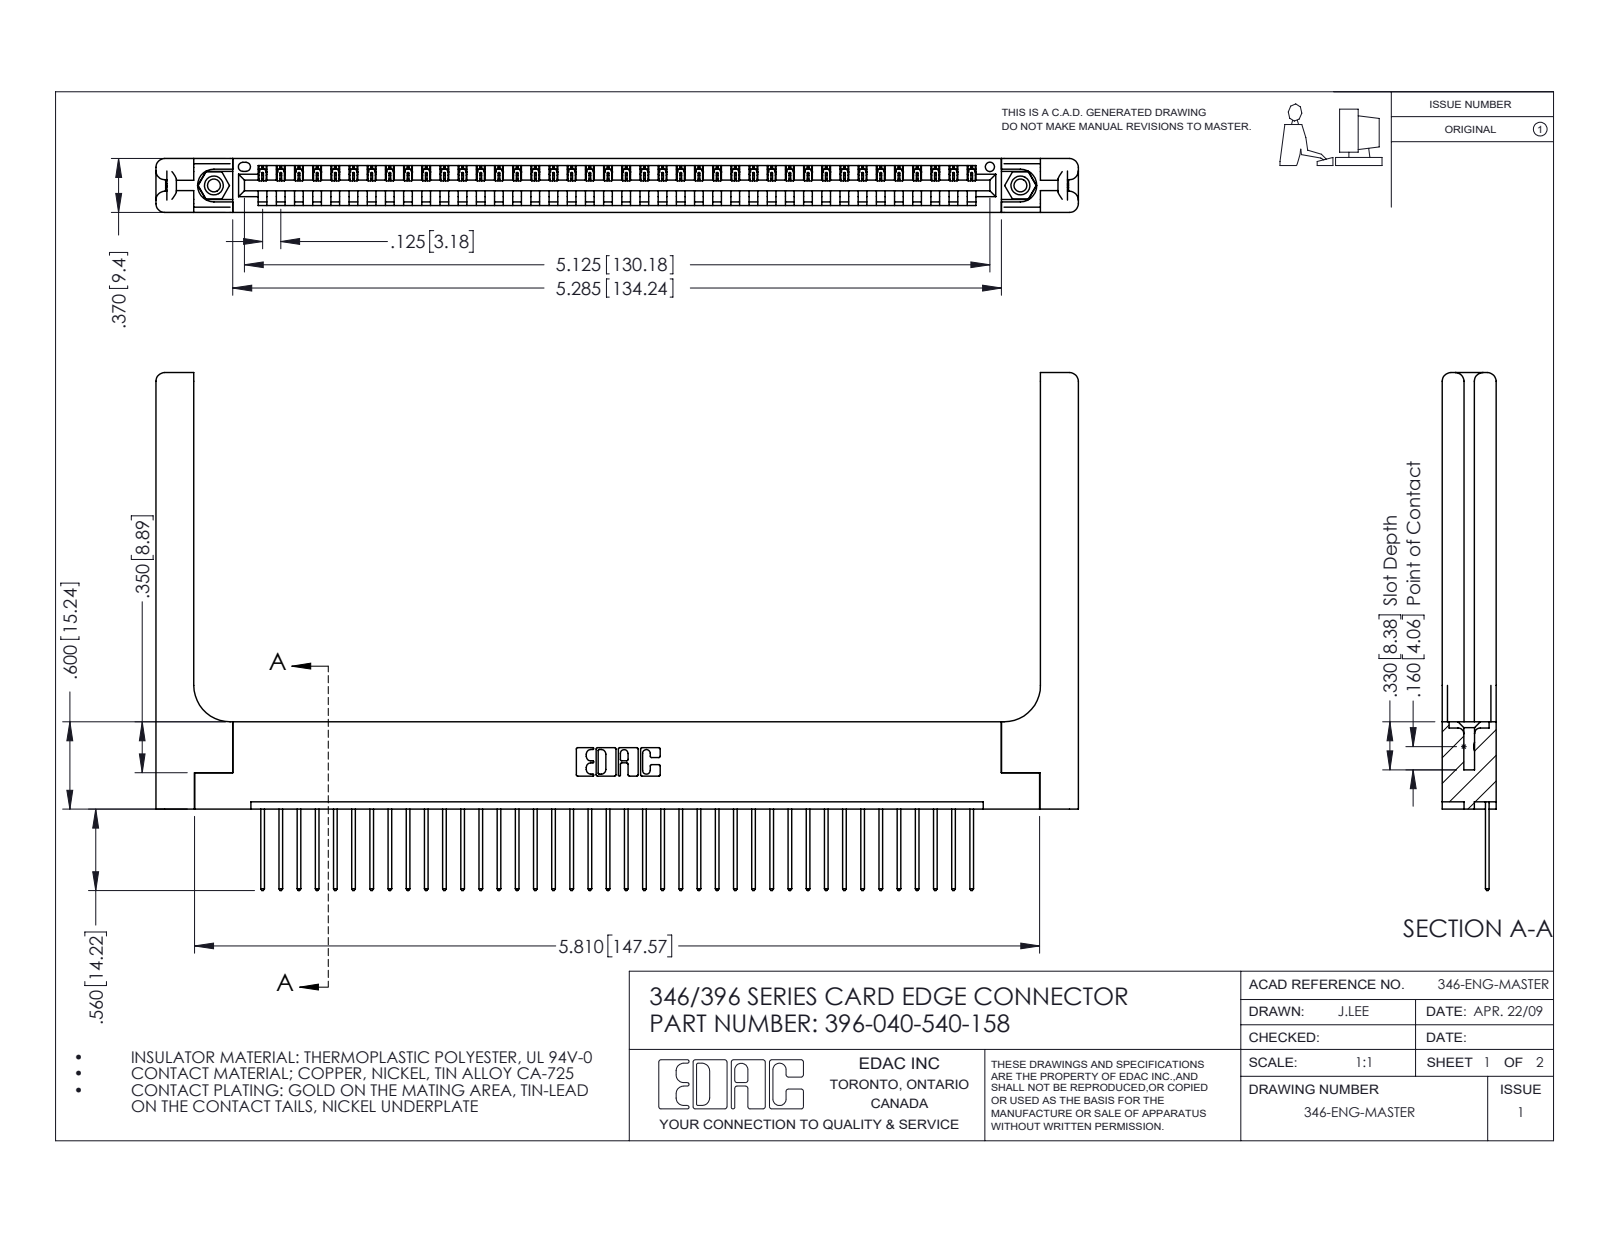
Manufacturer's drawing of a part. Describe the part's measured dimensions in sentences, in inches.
The part is named "345-292-001_345-293-140; 346 Part_Flush Mounting Lugs - 0.156 Dia-TH; 396-040-540-158; 345-250-001_345-250-001-102 (+1 more)". Its 3-D file was written by "SolidWorks 2016 (CONFIG_CONTROL_DESIGN)". It is 45 solids with 2698 faces: 1824 planar, 814 cylindrical and 60 other. Overall it measures 6.341 by 3.56 by 0.37 inches. Its volume is 1.402 cubic inches and its surface area 38.54 square inches. Round holes: 2 of diameter 0.089, 2 of diameter 0.125, 2 of diameter 0.156, 1 of diameter 0.064. Round bosses or shafts: 2 of diameter 0.155. Partial cylindrical surfaces (rounded edges, fillets, slot ends): 80 of radius 0.006, 80 of radius 0.01, 22 of radius 0.01, 16 of radius 0.06, 6 of radius 0.007, 6 of radius 0.031, 3 of radius 0.026, 2 of radius 0.03. The main face-to-face distances are 0.37, 0.048, 0.322, 0.072, 0.148, 0.15, 0.25, 0.298, 0.025, 0.222. The hole center spacings are 0.246, 5.336, 5.545.
